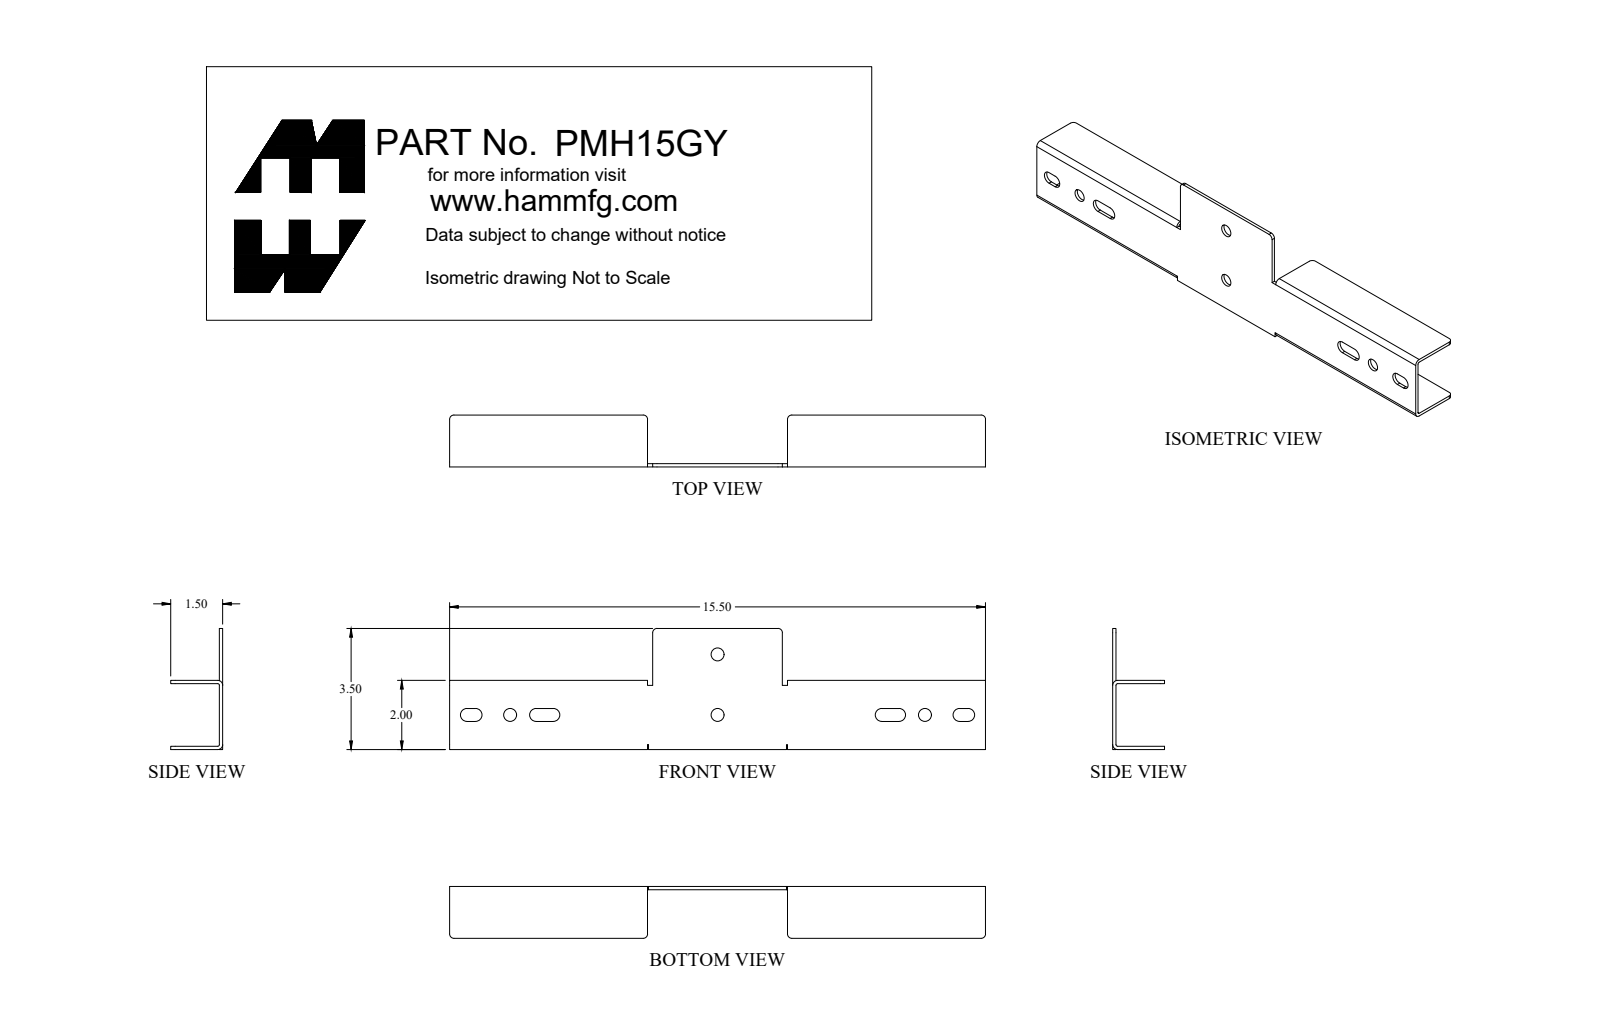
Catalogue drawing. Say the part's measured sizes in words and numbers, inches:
The part is named "PMH15GY". Its 3-D file was written by "SolidWorks 2018 (AUTOMOTIVE_DESIGN)". It is 1 solid with 72 faces: 38 planar, 34 cylindrical and 0 other. Overall it measures 15.5 by 3.5 by 1.5 inches. Its volume is 6.301 cubic inches and its surface area 138.5 square inches. Round holes: 4 of diameter 0.375. Partial cylindrical surfaces (rounded edges, fillets, slot ends): 8 of radius 0.188, 6 of radius 0.125, 2 of radius 0.048, 2 of radius 0.143. The main face-to-face distances are 0.095, 1.905, 2, 1.81, 1.5, 1.405, 5.725, 9.775, 15.5, 3.5. The hole center spacings are 6, 6.25, 1.75, 12.
